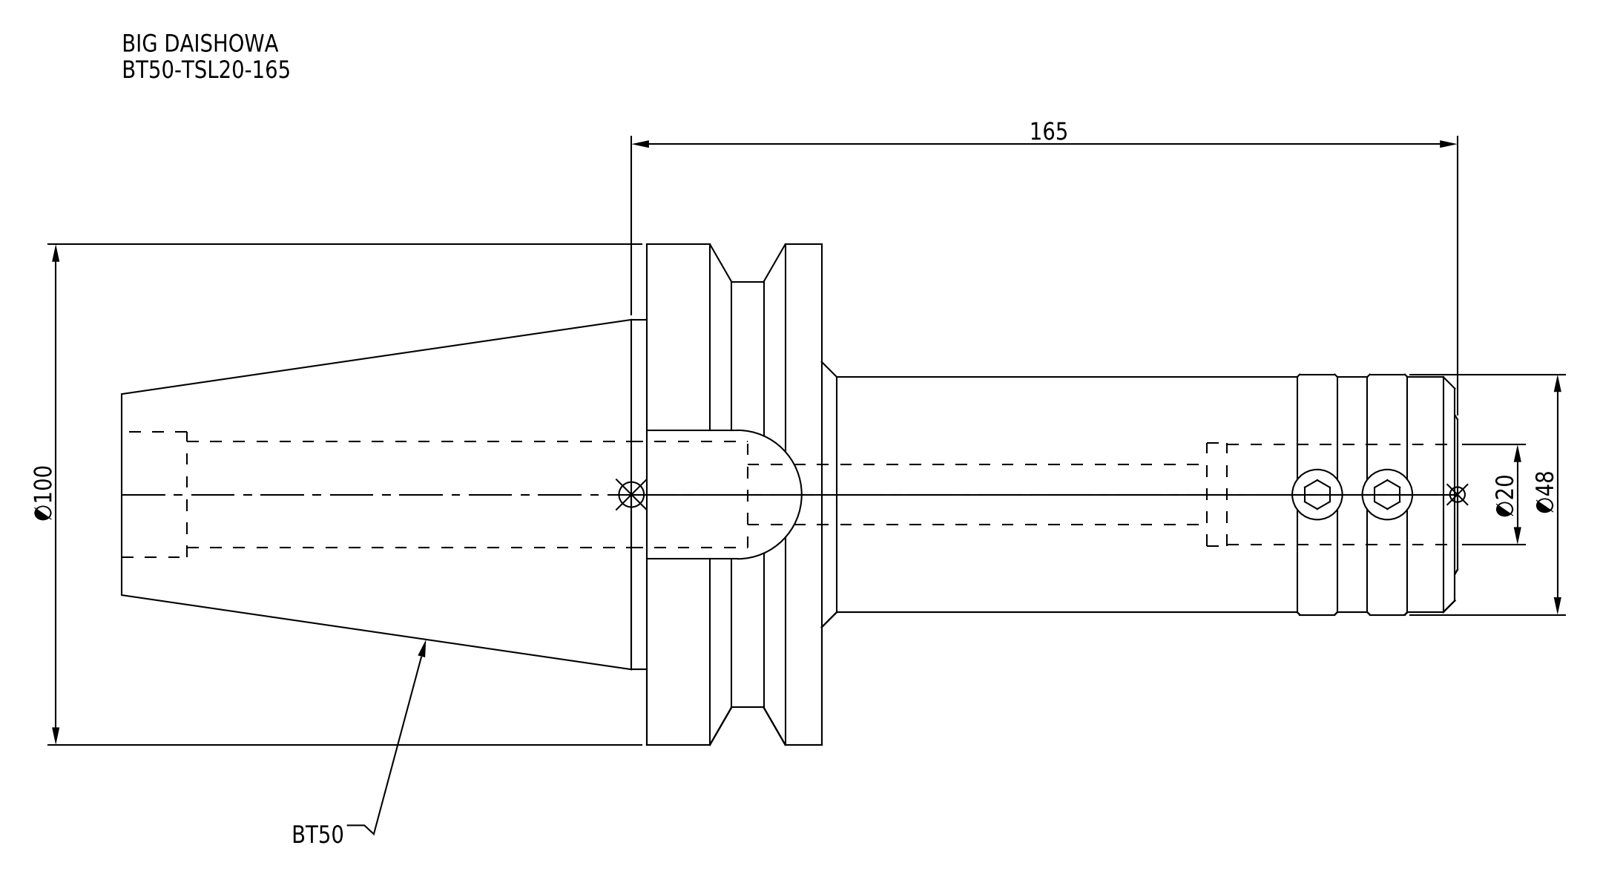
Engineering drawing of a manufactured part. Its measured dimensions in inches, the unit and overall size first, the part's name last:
Units: inches
Overall size (bounding box): 10.504 × 3.937 × 3.937
Round holes (diameter × count): ⌀0.472 ×1, ⌀0.787 ×1, ⌀0.811 ×1, ⌀0.835 ×1, ⌀0.984 ×1
Round bosses / shafts (diameter × count): ⌀3.937 ×1, ⌀3.346 ×1, ⌀2.75 ×1, ⌀1.89 ×1, ⌀1.85 ×1
Partial cylindrical surfaces — rounded edges, fillets, slot ends (radius × count): R0.506 ×1
Main face-to-face distances: 1.378, 5.504, 4.126, 2.787, 4.98, 6.358, 10.484, 1.012, 0.02, 5
Volume: 39.25 in³ · Surface area: 121.6 in²
Bodies: 1 solid, 67 faces (15 planar, 32 cylindrical, 20 other)
Part name (STEP PRODUCT): BT50-TSL20-165
STEP written by: CREO PARAMETRIC BY PTC INC, 2016380 (AUTOMOTIVE_DESIGN)
